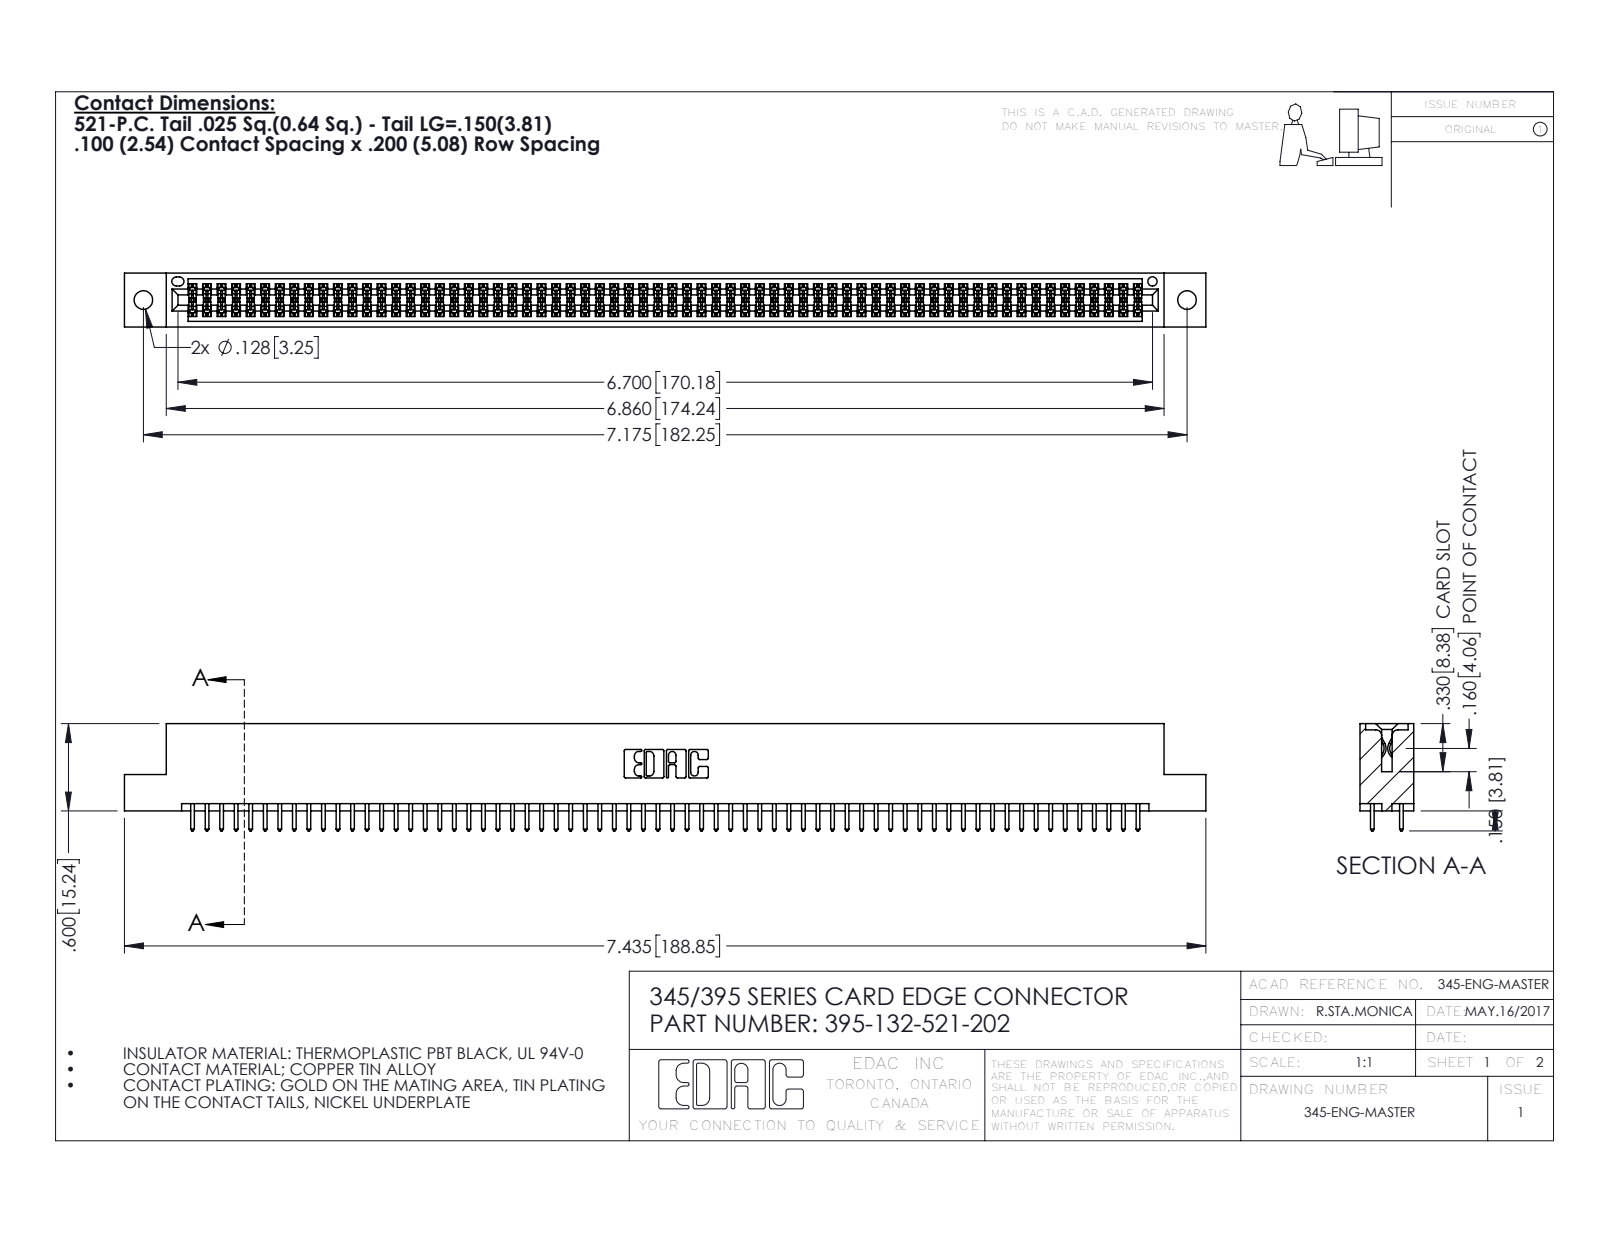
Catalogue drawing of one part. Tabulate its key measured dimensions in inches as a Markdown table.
| quantity | value |
| --- | --- |
| part name | 345-292-001_345-293-121; 395-132-521-202; 345 Part_Flush Mounting Lugs - 0.128 Dia |
| STEP written by | SolidWorks 2016 (CONFIG_CONTROL_DESIGN) |
| units | inches |
| bodies | 133 solids, 6726 faces (4436 planar, 2290 cylindrical, 0 other) |
| overall size | 7.435 × 0.737 × 0.37 |
| volume | 1.128 in³ |
| surface area | 42.09 in² |
| round holes (diameter × count) | 0.128 × 2, 0.064 × 1 |
| partial cylindrical surfaces (radius × count) | 0.006 × 198, 0.01 × 132, 0.01 × 22, 0.007 × 6, 0.031 × 6, 0.026 × 3, 0.014 × 2, 0.019 × 2 |
| main face-to-face distances | 0.298, 0.072, 0.2, 0.098, 0.272, 0.025, 0.37, 0.225, 0.175, 0.149 |
| hole center spacings | 0.27, 6.939, 7.175 |
